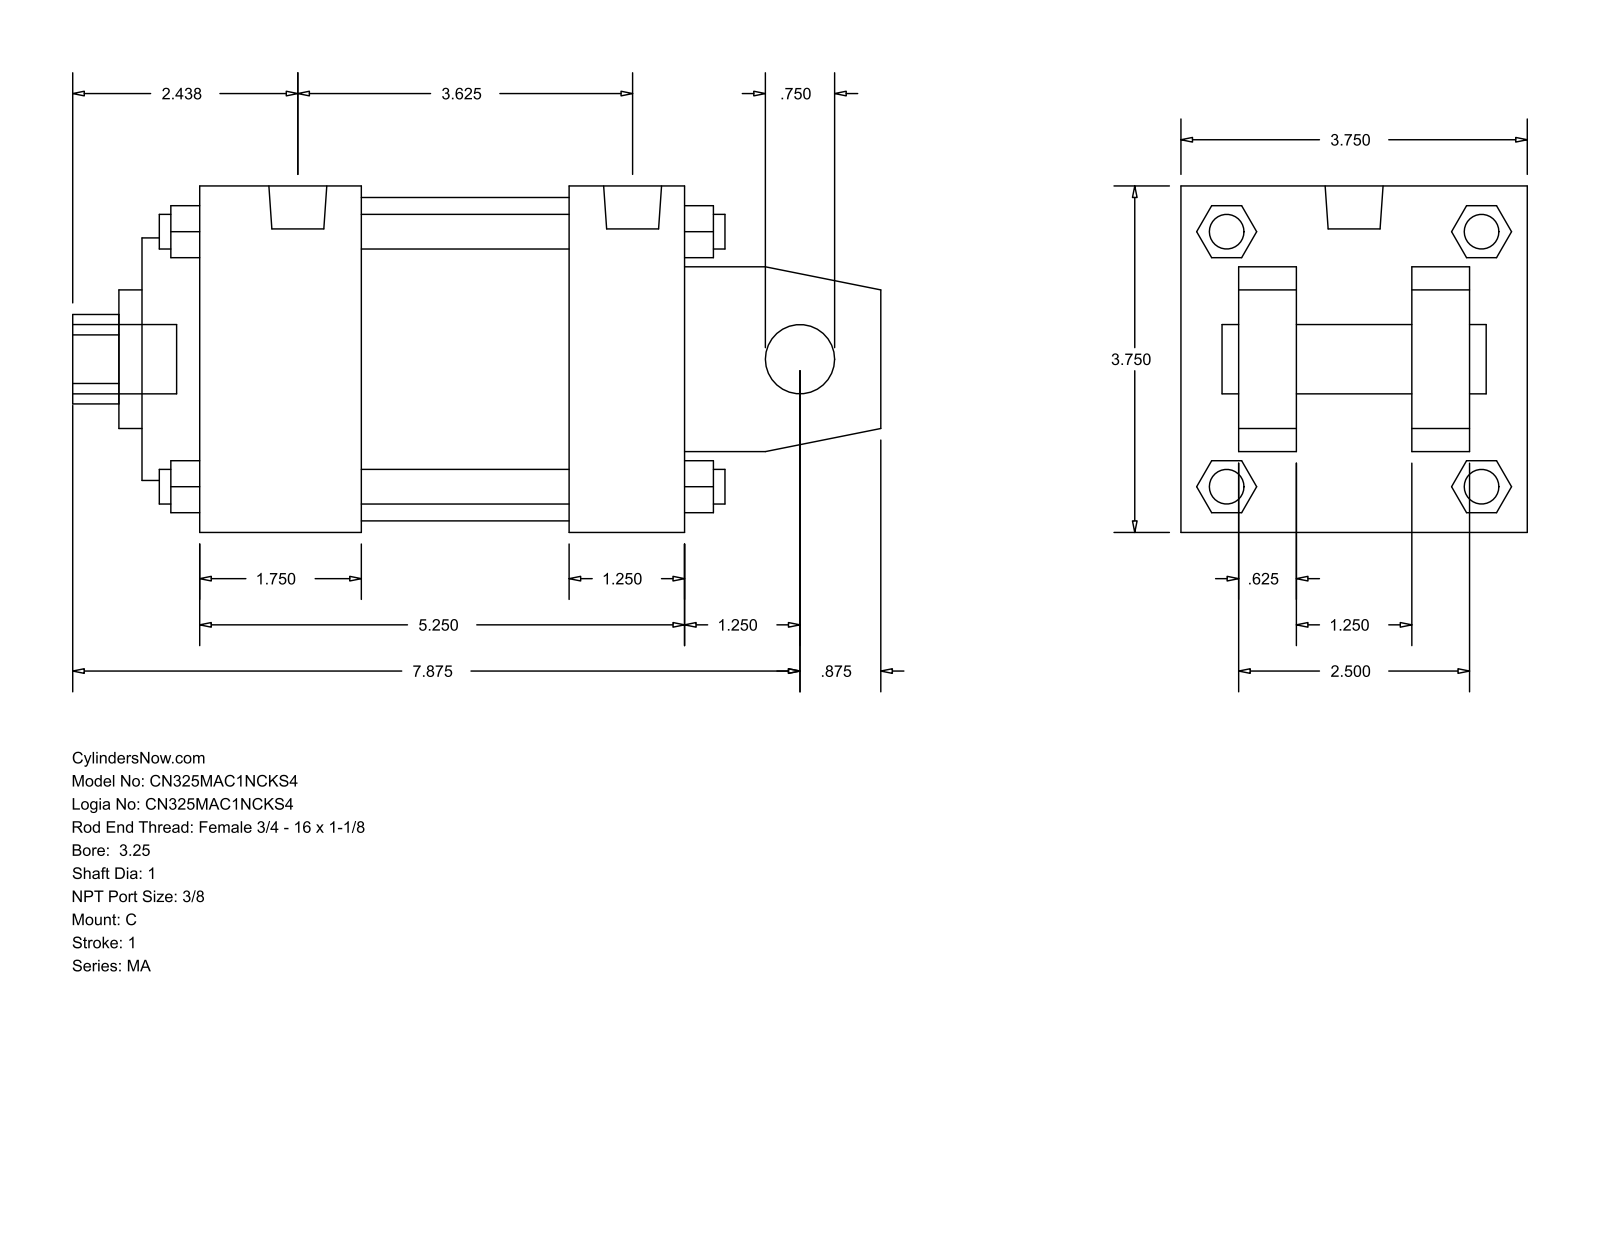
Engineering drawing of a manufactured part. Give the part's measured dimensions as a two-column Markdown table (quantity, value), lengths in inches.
| quantity | value |
| --- | --- |
| part name | MA_C__0325_1 |
| STEP written by | GSSL Pune (CONFIG_CONTROL_DESIGN) |
| units | inches |
| bodies | 0 solids, 141 faces (109 planar, 32 cylindrical, 0 other) |
| overall size | 8.75 × 3.75 × 3.75 |
| round holes (diameter × count) | 0.75 × 1, 1 × 1, 1.5 × 1, 2.625 × 1, 3.5 × 1 |
| round bosses / shafts (diameter × count) | 0.437 × 4, 0.375 × 4, 0.627 × 2, 0.75 × 1 |
| partial cylindrical surfaces (radius × count) | 0.484 × 1 |
| main face-to-face distances | 3.75, 0.625, 2.5, 5.25, 1.25, 3.125, 1.875, 4, 1.25, 1.75 |
